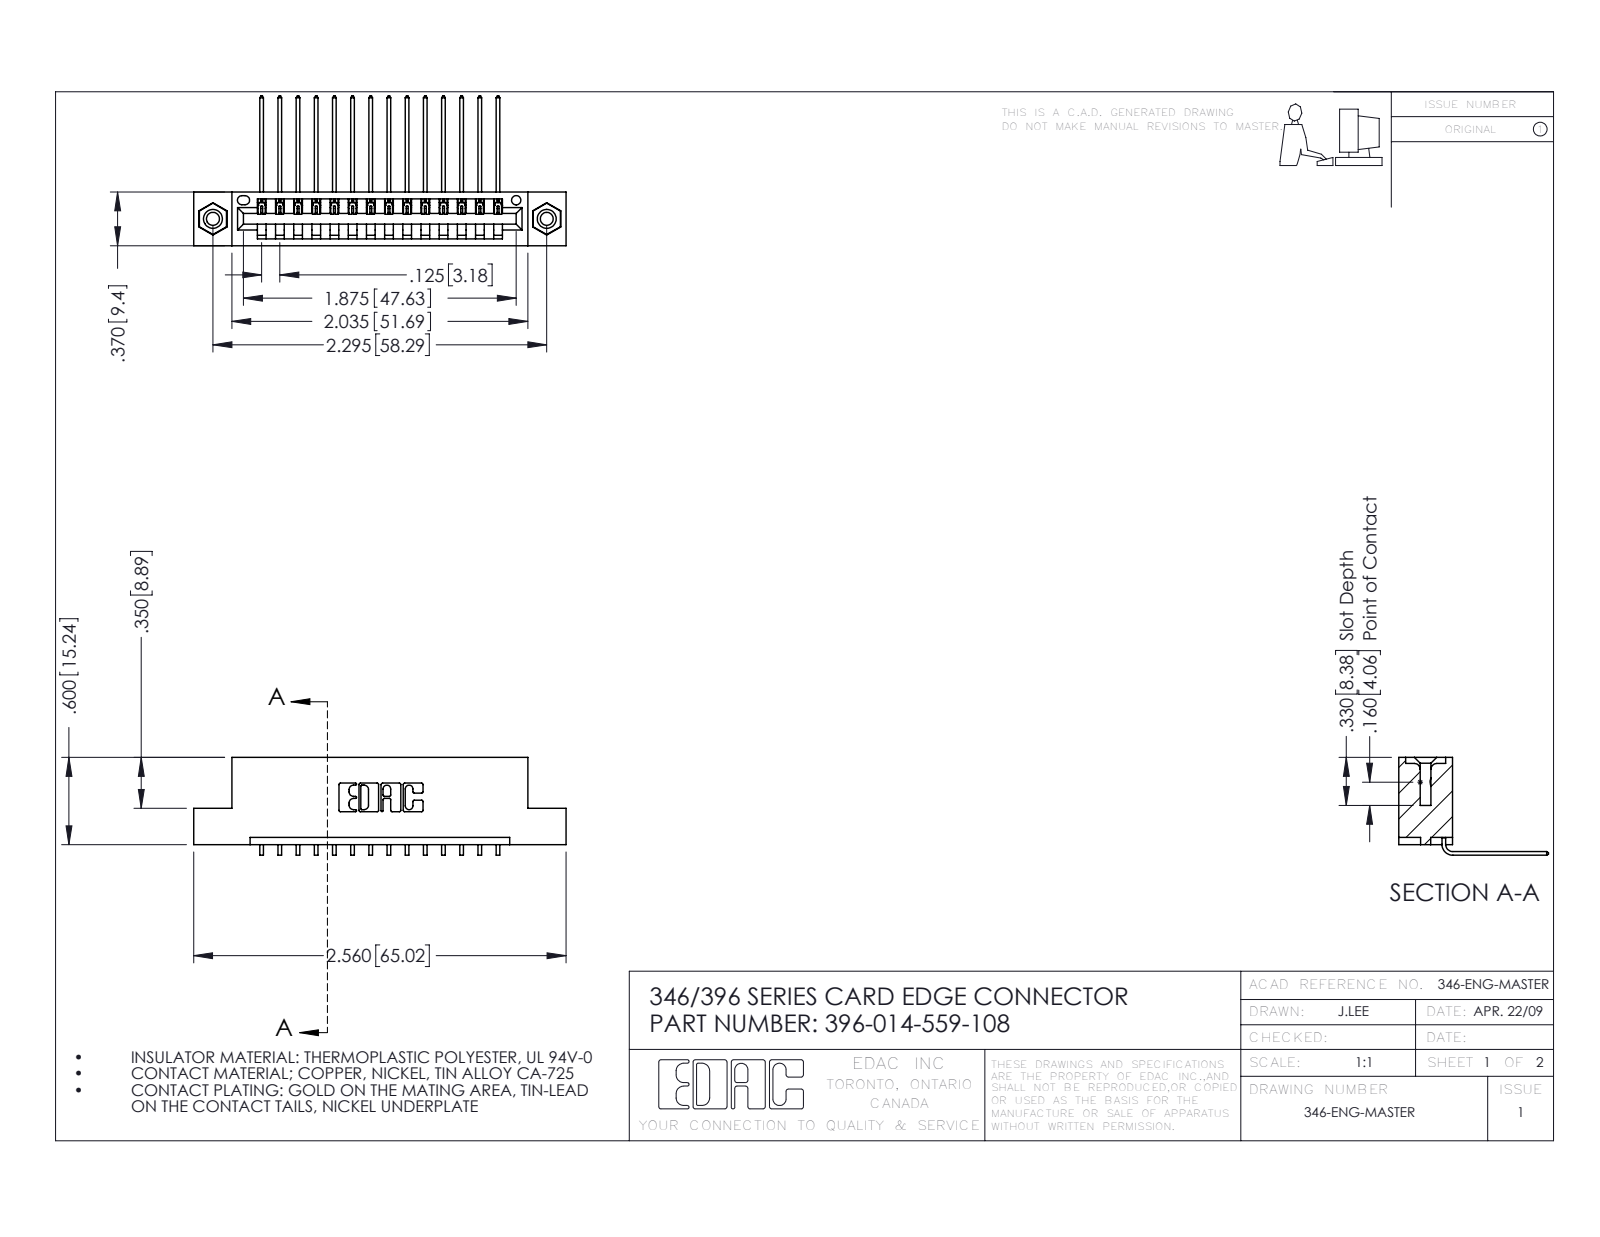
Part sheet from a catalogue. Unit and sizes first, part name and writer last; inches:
Units: inches
Overall size (bounding box): 2.56 × 1.03 × 0.673
Round holes (diameter × count): ⌀0.089 ×2, ⌀0.125 ×2, ⌀0.156 ×2, ⌀0.064 ×1
Round bosses / shafts (diameter × count): ⌀0.155 ×2
Partial cylindrical surfaces — rounded edges, fillets, slot ends (radius × count): R0.006 ×28, R0.01 ×22, R0.007 ×6, R0.031 ×6, R0.026 ×3, R0.031 ×2, R0.04 ×2, R0.014 ×1
Main face-to-face distances: 0.048, 0.322, 0.25, 0.37, 0.072, 0.025, 0.298, 0.148, 0.222, 0.1
Hole centre spacings: 0.246, 2.089, 2.295
Volume: 0.371 in³ · Surface area: 11.76 in²
Bodies: 17 solids, 1022 faces (696 planar, 310 cylindrical, 16 other)
Part name (STEP PRODUCT): 346 Part_Flush Mounting Lugs - 0.156 Dia-TI; 345-250-001_345-250-003-102; 345-292-001_558 559 Tail - 1; 396-014-559-108
STEP written by: SolidWorks 2016 (CONFIG_CONTROL_DESIGN)
